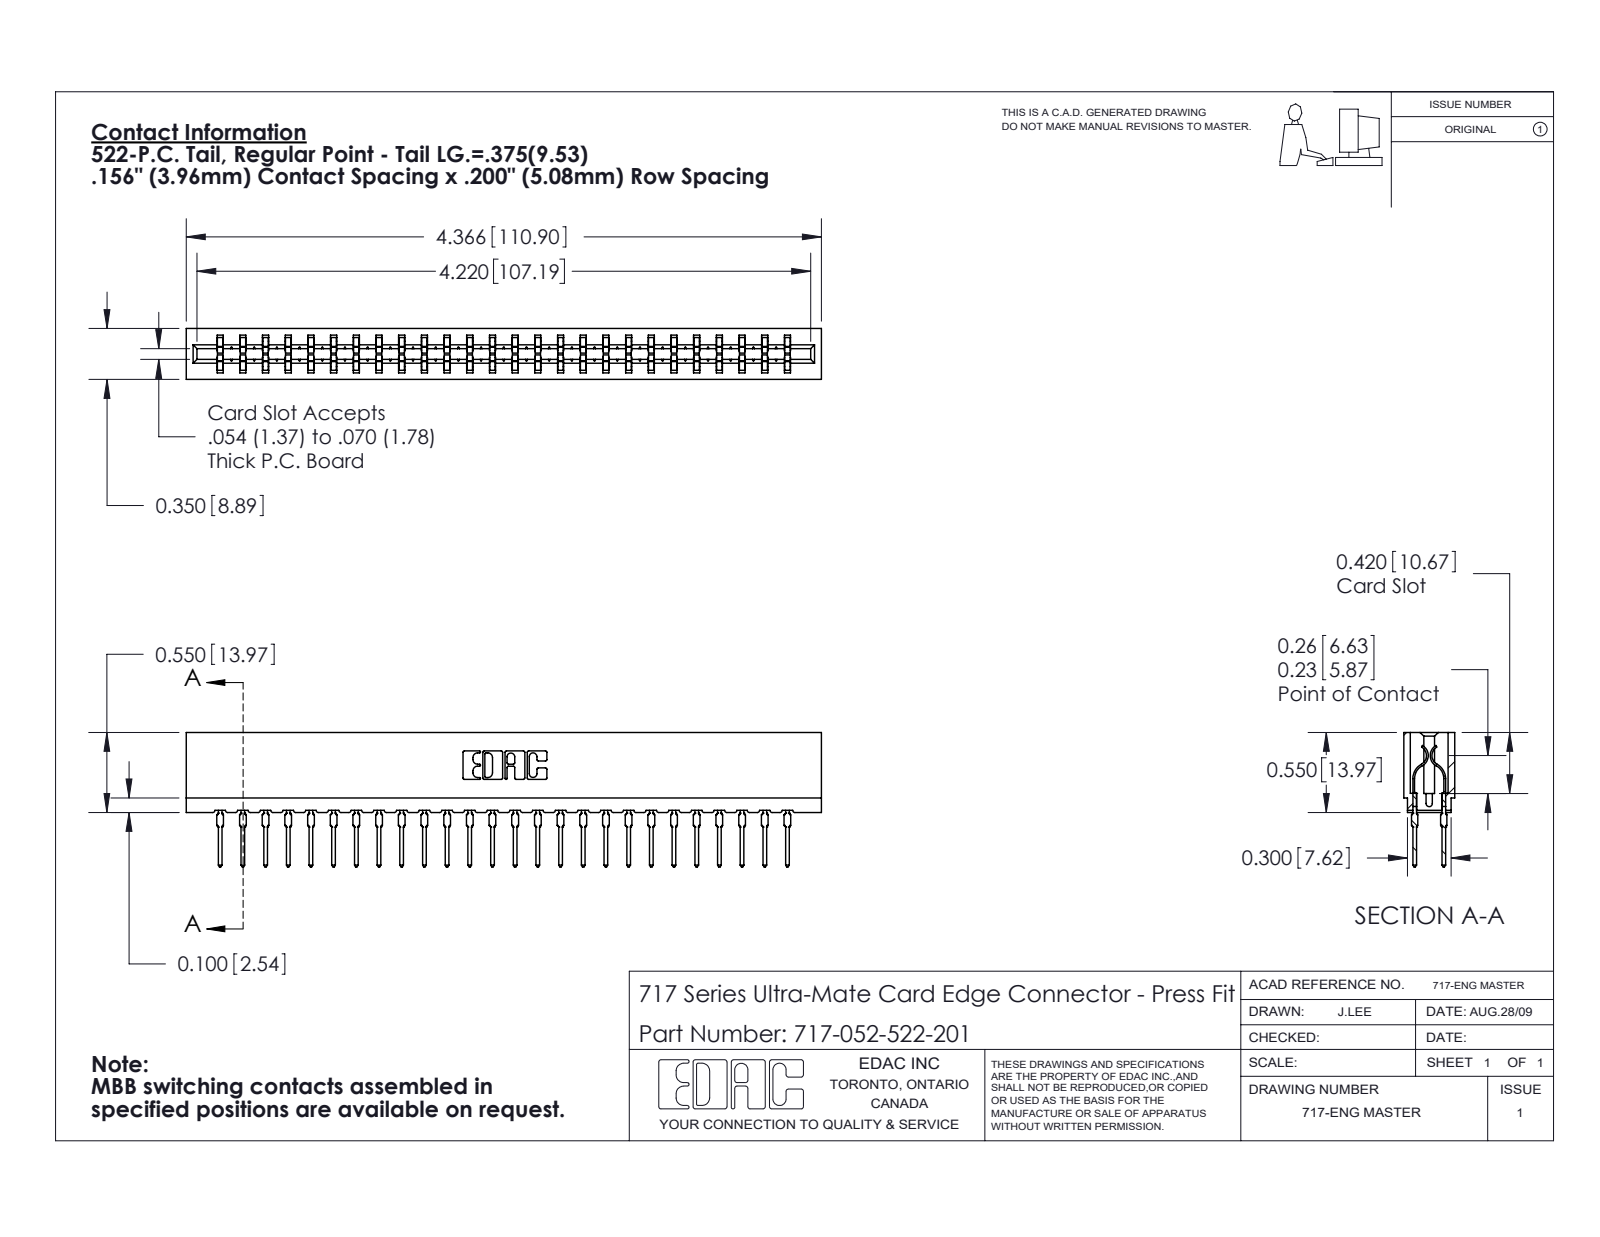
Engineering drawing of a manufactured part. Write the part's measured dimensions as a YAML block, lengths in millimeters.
part_name: "745-292-001_522; 717-052-522-201; 717 Part_Insulator Option - 06"
step_written_by: "SolidWorks 2020 (CONFIG_CONTROL_DESIGN)"
units: millimeters
bodies: {solids: 53, faces: 4774, planar: 2472, cylindrical: 950, other: 1352}
overall_size: [110.9, 23.5, 8.9]
volume: 9730
surface_area: 14880
partial_cylinders:
  - {radius: 0.5, count: 104}
  - {radius: 0.4, count: 52}
  - {radius: 0.3, count: 22}
  - {radius: 0.1, count: 8}
  - {radius: 0.3, count: 8}
  - {radius: 0.2, count: 6}
  - {radius: 0.8, count: 6}
  - {radius: 0.7, count: 3}
face_to_face_distances: [5.4, 3.5, 8.9, 1.6, 7.3, 1.9, 3.8, 4, 1.9, 1.1]
